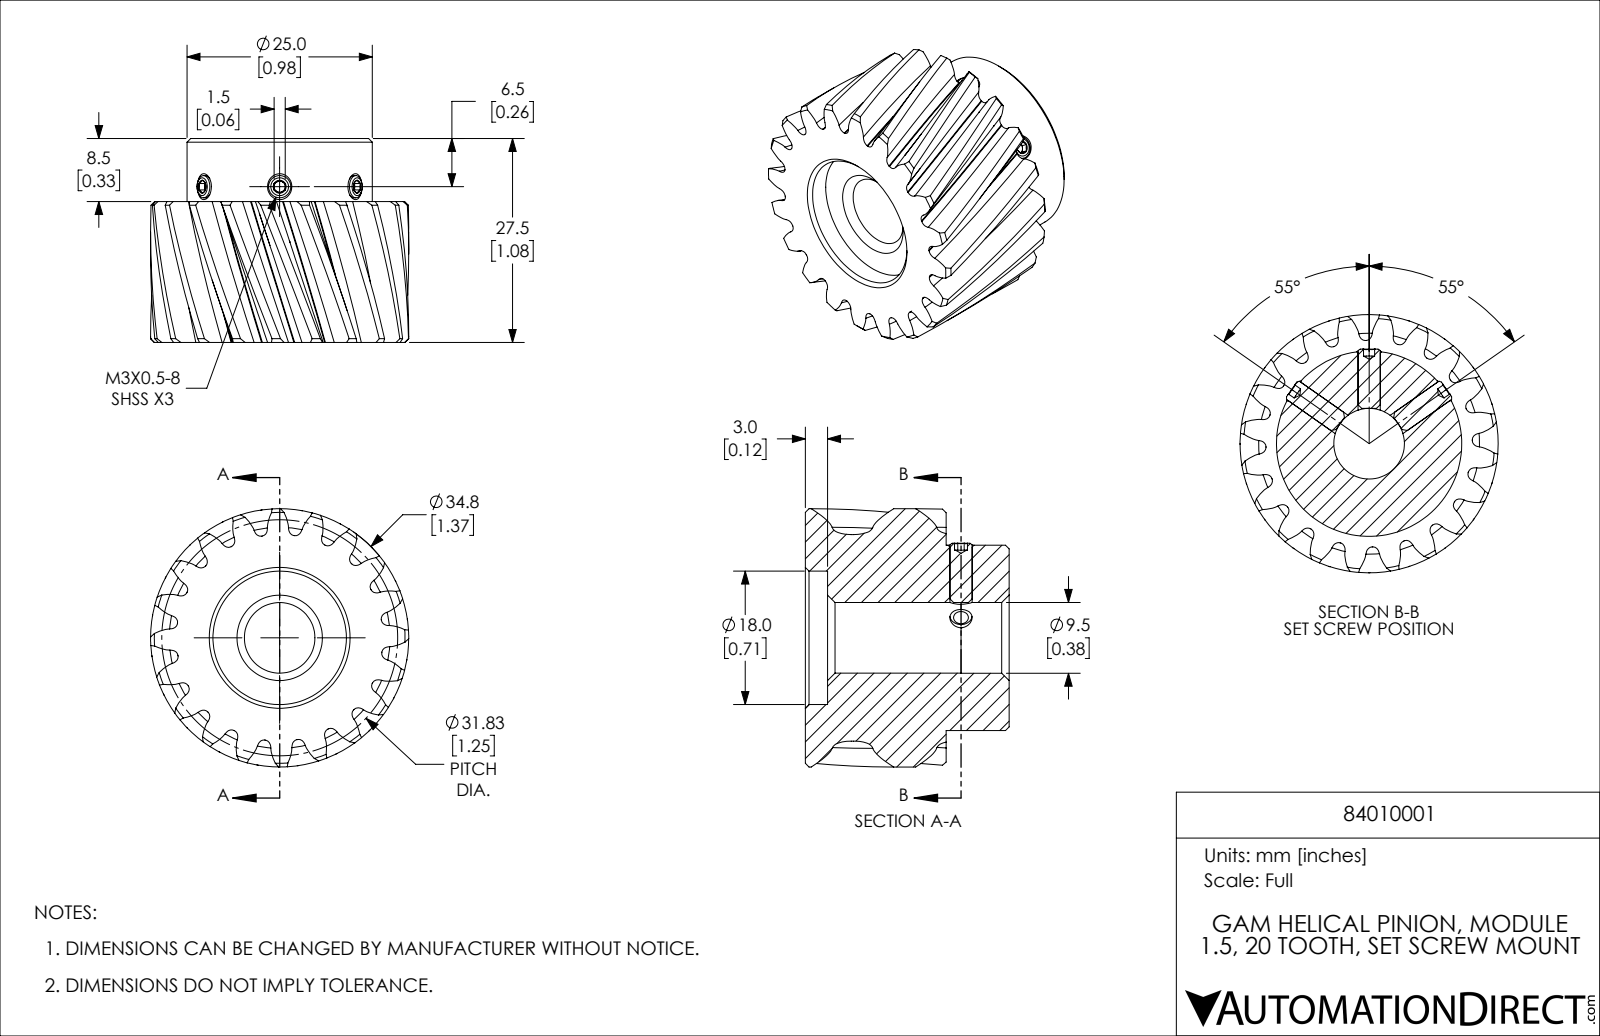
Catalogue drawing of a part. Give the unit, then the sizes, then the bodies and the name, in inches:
Units: inches
Overall size (bounding box): 1.371 × 1.371 × 1.083
Round holes (diameter × count): ⌀0.118 ×3, ⌀0.375 ×1, ⌀0.376 ×1, ⌀0.709 ×1
Round bosses / shafts (diameter × count): ⌀0.118 ×2, ⌀1.371 ×1, ⌀0.984 ×1
Main face-to-face distances: 1.083, 0.748, 0.335, 0.118, 0.63, 0.965, 0.059, 0.315, 0.114, 0.744
Volume: 1.005 in³ · Surface area: 11.02 in²
Bodies: 4 solids, 500 faces (173 planar, 42 cylindrical, 285 other)
Part name (STEP PRODUCT): 84010001
STEP written by: SolidWorks 2019 (CONFIG_CONTROL_DESIGN)
